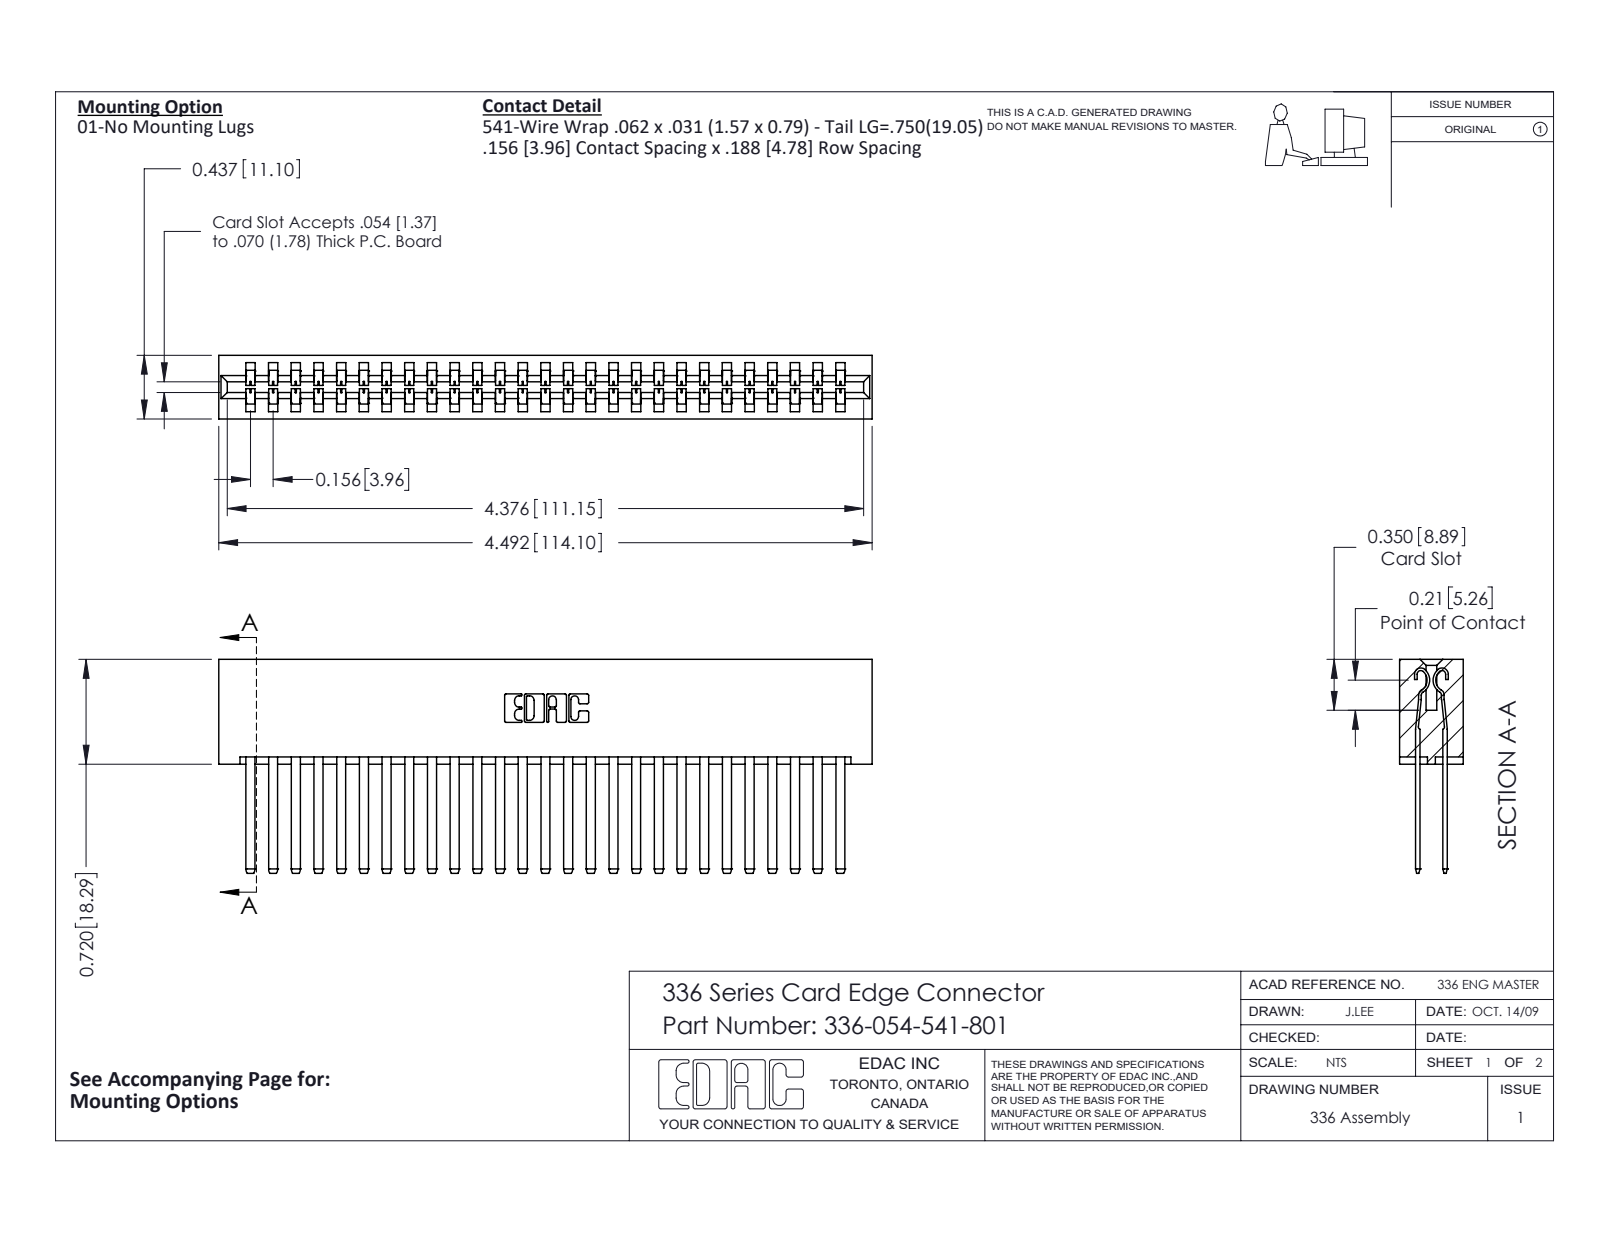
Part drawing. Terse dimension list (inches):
name: 336-290-001_336-290-541; 336 Part_Lugless; 336-054-541-801
written by: SolidWorks 2020 (CONFIG_CONTROL_DESIGN)
unit: in
bodies: 55 solids, 2374 faces (1470 planar, 904 cylindrical, 0 other)
size: 4.492 × 1.47 × 0.437
volume: 1.149 in³; area: 37.16 in²
rounds: 108× R0.004, 54× R0.056, 22× R0.01, 6× R0.007, 6× R0.031, 4× R0.022, 4× R0.04, 3× R0.026
face distances: 0.188, 0.328, 0.14, 0.297, 0.109, 0.031, 0.437, 0.033, 0.181, 0.256
